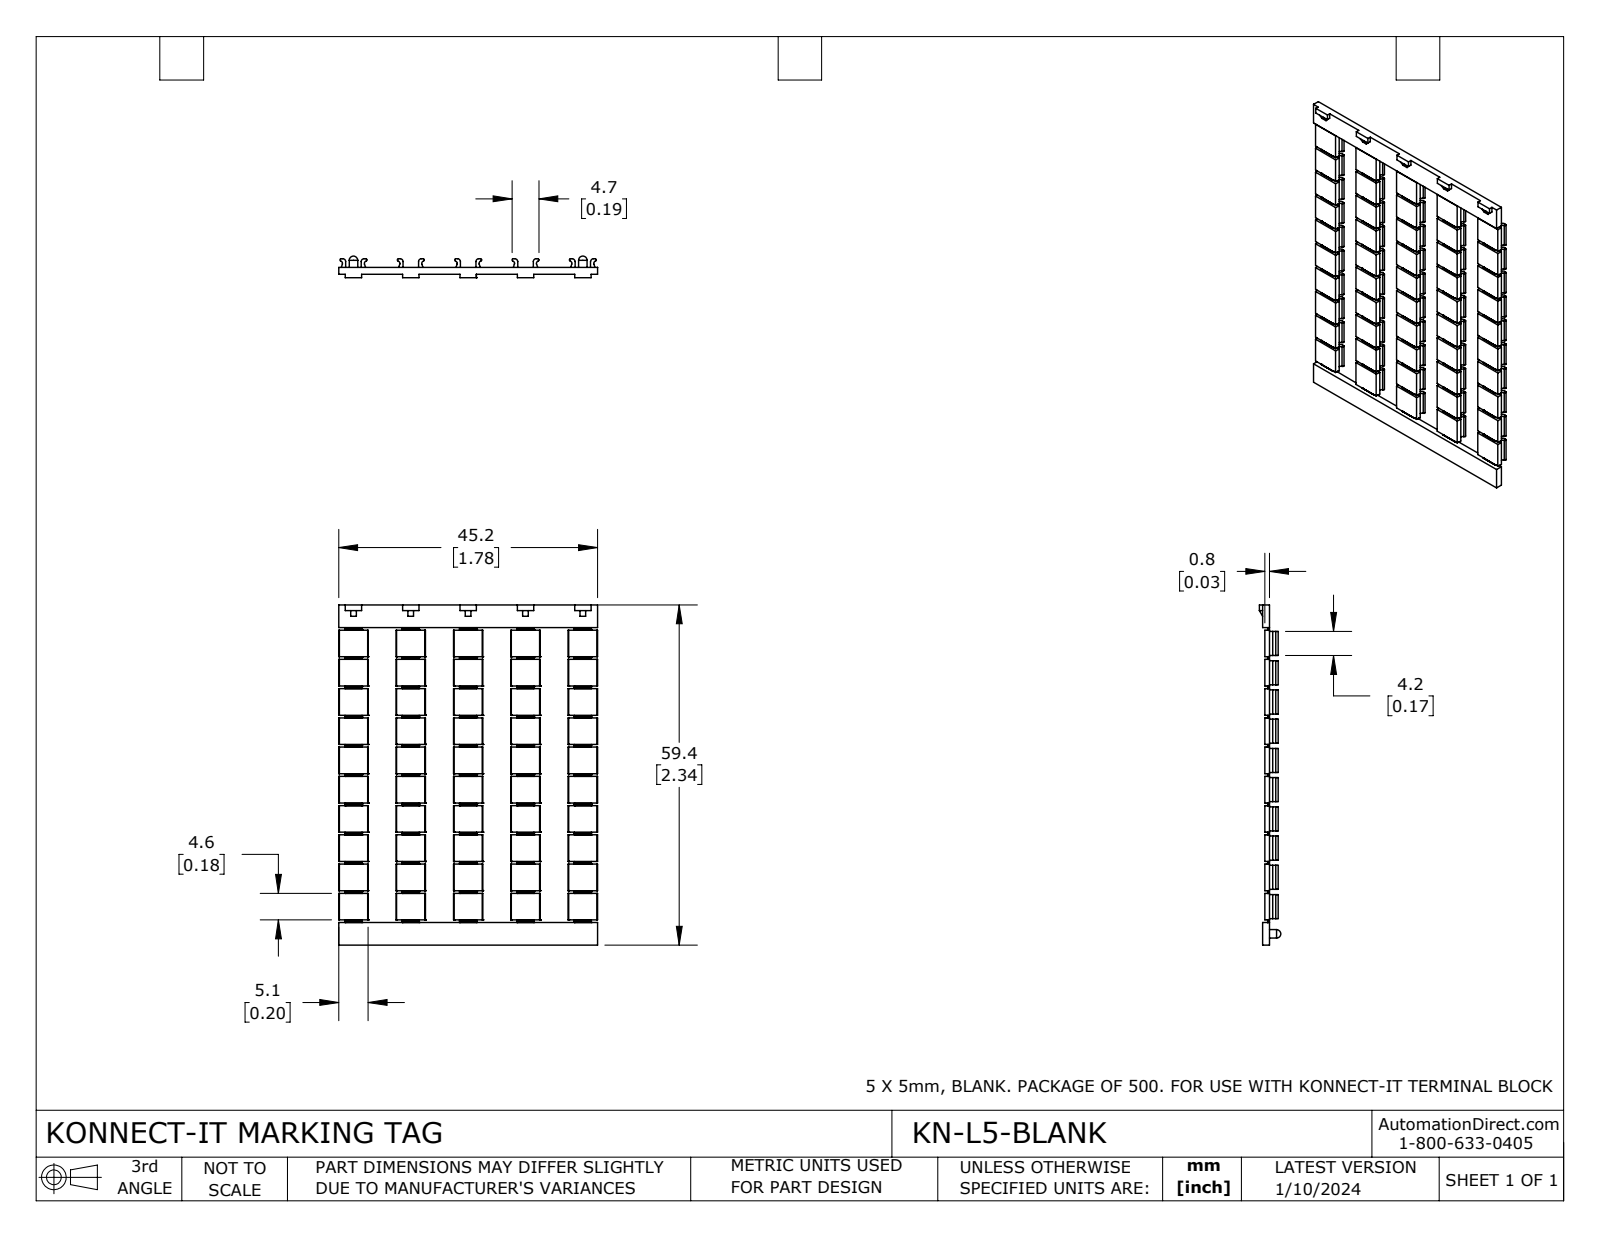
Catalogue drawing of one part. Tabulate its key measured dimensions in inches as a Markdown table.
| quantity | value |
| --- | --- |
| part name | KN-L5-BLANK |
| STEP written by | SolidWorks 2023 (CONFIG_CONTROL_DESIGN) |
| units | inches |
| bodies | 1 solid, 2023 faces (1507 planar, 514 cylindrical, 2 other) |
| overall size | 2.338 × 1.779 × 0.146 |
| volume | 0.113 in³ |
| surface area | 8.869 in² |
| round bosses / shafts (diameter × count) | 0.058 × 2 |
| partial cylindrical surfaces (radius × count) | 0.007 × 11, 0.009 × 10, 0.016 × 10, 0.02 × 10 |
| main face-to-face distances | 0.032, 0.047, 0.015, 0.394, 0.789, 0.391, 0.783, 0.107, 0.201, 0.603 |
